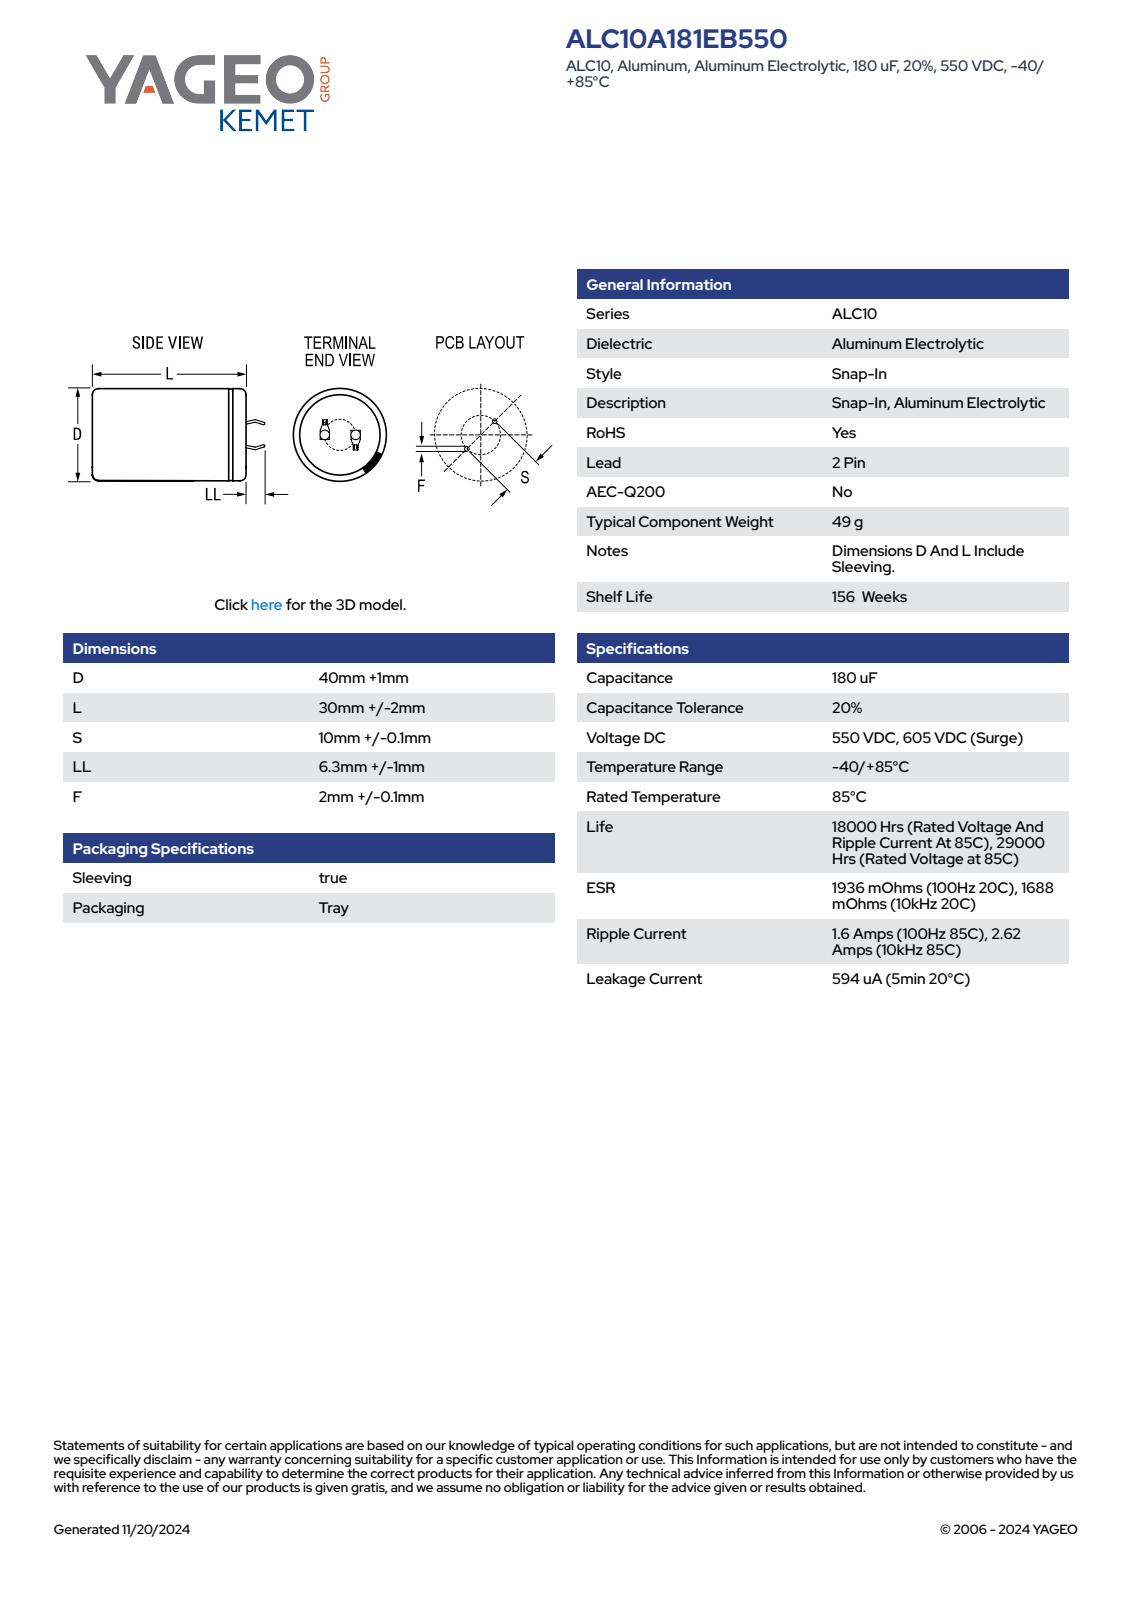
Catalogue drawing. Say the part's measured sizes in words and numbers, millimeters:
The part is named "CARS_K2P_40X30_D41L32S10LL7.3F2.1". Its 3-D file was written by "SolidWorks 2014 (AUTOMOTIVE_DESIGN)". It is 1 solid with 100 faces: 52 planar, 9 cylindrical and 39 other. Overall it measures 41 by 41 by 39.29 millimeters. Its volume is 41 463 cubic millimeters and its surface area 6 745 square millimeters. Round holes: 1 of diameter 36.28. Round bosses or shafts: 1 of diameter 41. Partial cylindrical surfaces (rounded edges, fillets, slot ends): 1 of radius 20.49. The main face-to-face distances are 31.99, 0.6, 32.49, 0.5, 7.08, 7.64, 0.75, 1.35, 7.68, 6.48.
